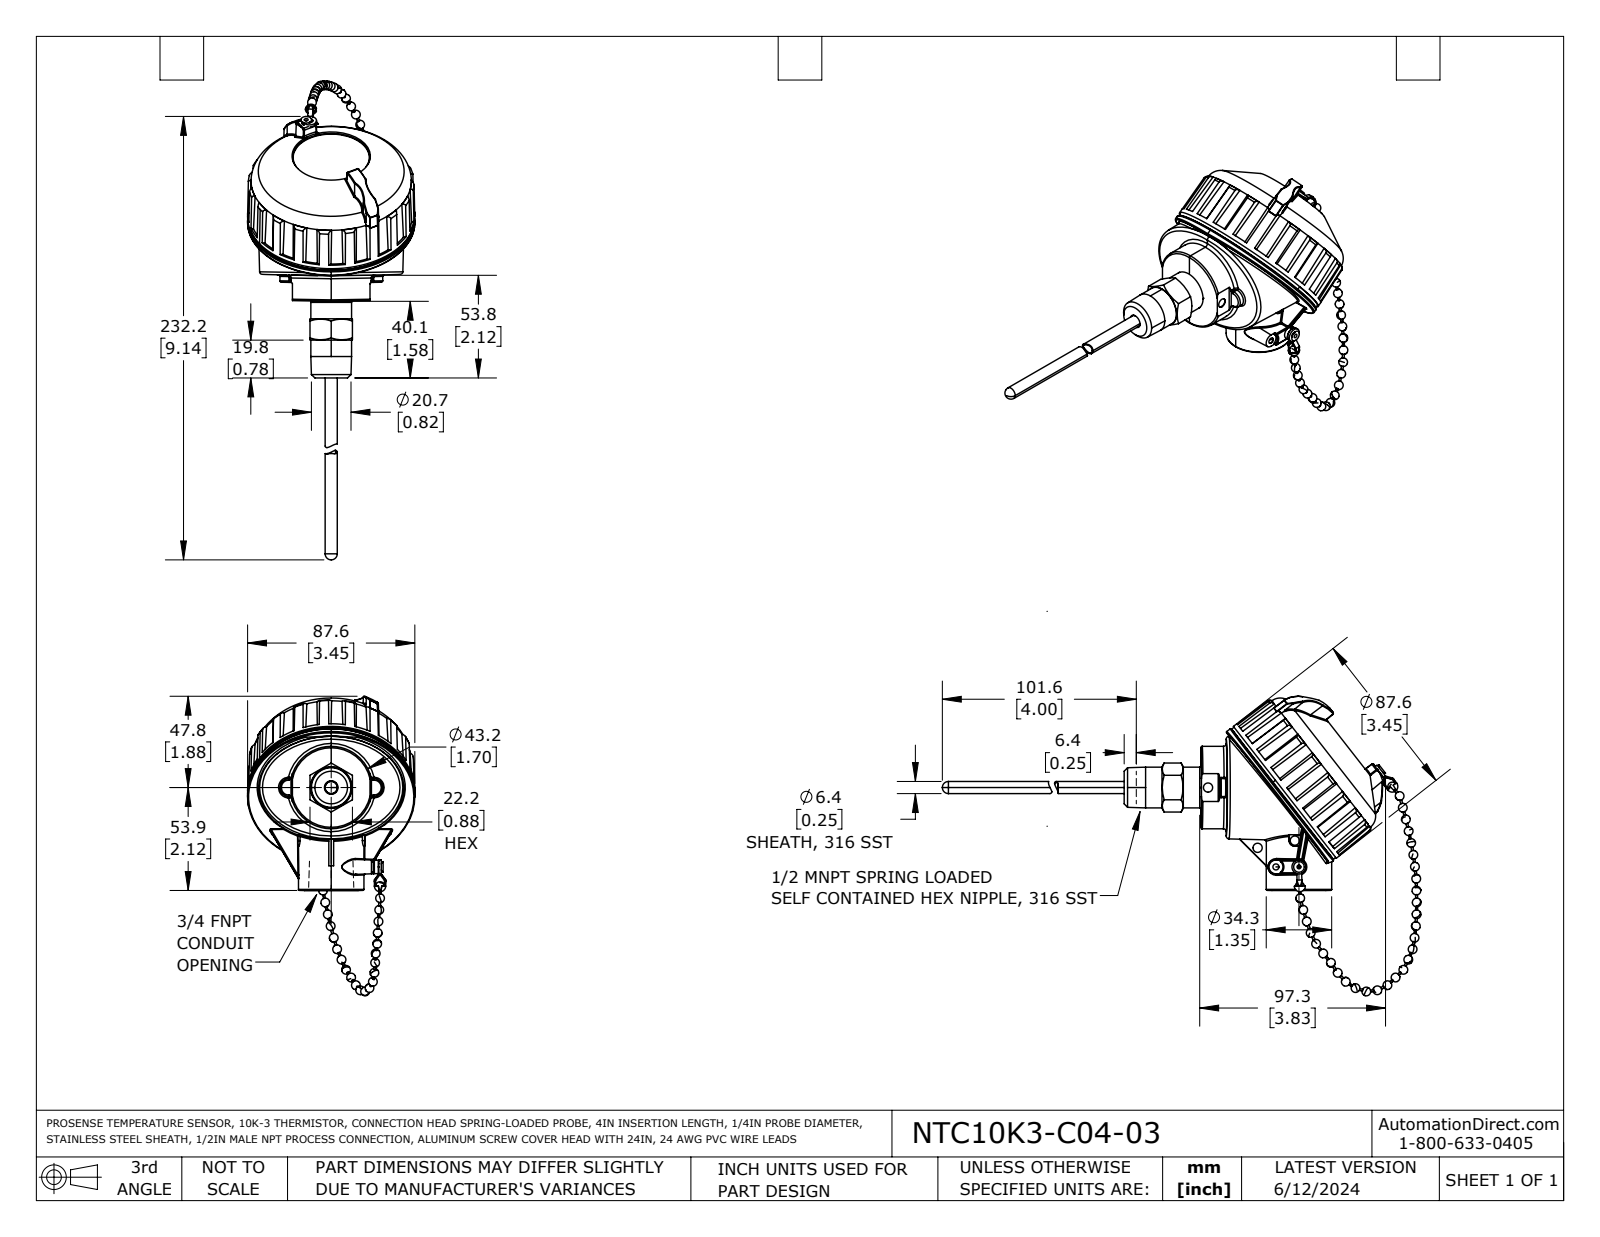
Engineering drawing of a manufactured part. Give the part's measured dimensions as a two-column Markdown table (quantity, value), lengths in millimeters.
| quantity | value |
| --- | --- |
| part name | NTC10K3-C04-03 |
| STEP written by | SolidWorks 2021 (AUTOMOTIVE_DESIGN) |
| units | millimeters |
| bodies | 10 solids, 991 faces (234 planar, 195 cylindrical, 562 other) |
| overall size | 250.7 × 156.9 × 87.6 |
| volume | 153 000 mm³ |
| surface area | 78 130 mm² |
| round holes (diameter × count) | 4.8 × 3, 2 × 2, 3.7 × 2, 3.2 × 1, 4.2 × 1, 5.3 × 1, 6.6 × 1, 11.1 × 1, 11.8 × 1, 22.6 × 1, 76.3 × 1, 76.9 × 1 |
| round bosses / shafts (diameter × count) | 1 × 31, 7.4 × 2, 3.1 × 2, 87.6 × 1, 86.5 × 1, 79.3 × 1, 76 × 1, 43.2 × 1 |
| partial cylindrical surfaces (radius × count) | 0.5 × 21, 0.8 × 11, 0.4 × 6, 1.5 × 5, 1.6 × 2, 4.7 × 2, 3.7 × 1 |
| main face-to-face distances | 36.1, 37.7, 1.6, 3.6, 39.6, 41.2, 13.3, 13.3, 14.9, 27.6 |
| hole center spacings | 25, 1.8, 12.1, 13.9, 13.9, 17, 19.9, 23.9 |
